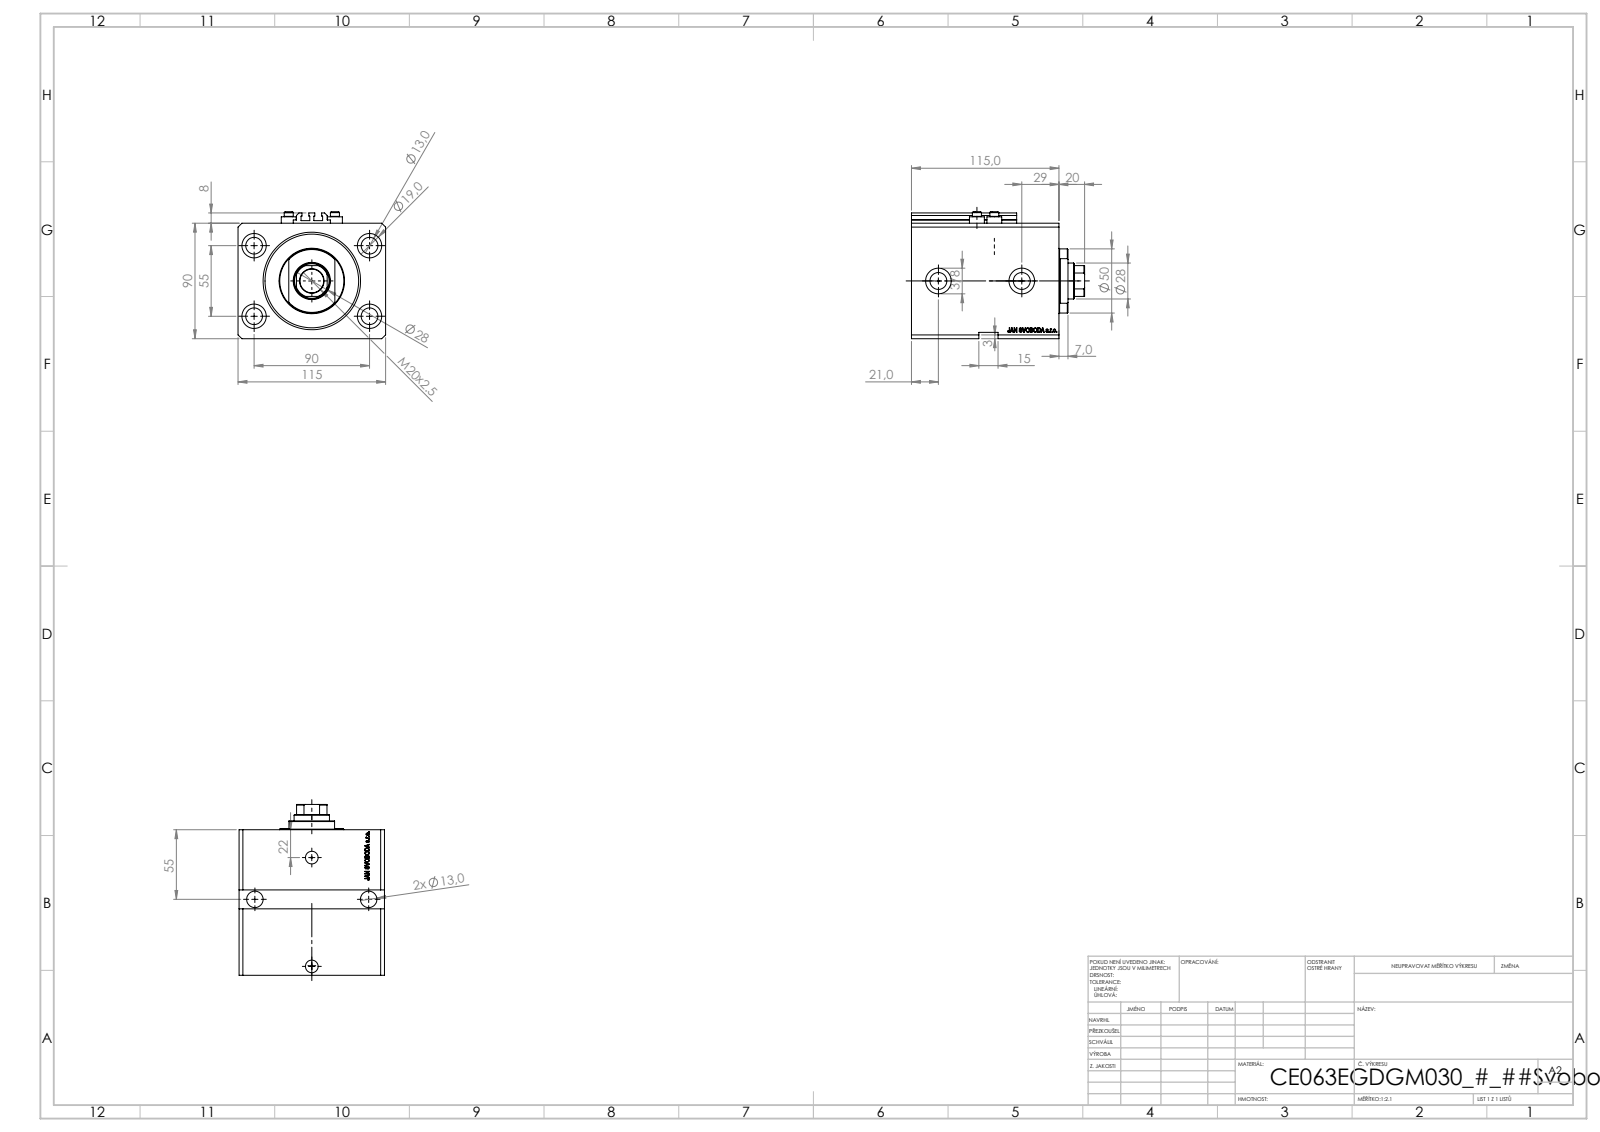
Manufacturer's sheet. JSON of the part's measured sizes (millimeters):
{"part_name": "V250CE_VC_E; ALLEN BOLT V250CE; V250CE_C_VCP; V250CE_E_Body", "step_written_by": "SolidWorks 2019 (CONFIG_CONTROL_DESIGN)", "units": "millimeters", "bodies": {"solids": 8, "faces": 1123, "planar": 547, "cylindrical": 138, "other": 438}, "overall_size": [135, 115, 99], "volume_mm3": 1025000, "surface_area_mm2": 164663, "round_holes": [[13, 6], [1.25, 4], [4, 4], [19, 4], [10, 2], [13.16, 2], [20, 2], [18.5, 1], [28, 1], [63, 1], [76, 1]], "round_bosses_or_shafts": [[11.6, 4], [7, 4], [50, 1]], "partial_cylinders_radius": [[0.2, 10], [13.5, 1]], "face_to_face_distances": [115, 90, 97.1, 20, 17.9, 95, 77.1, 30, 65, 47.1], "hole_center_spacings": [52.74, 90, 13.6, 27.39, 28.46, 33.62, 36, 38.48]}
